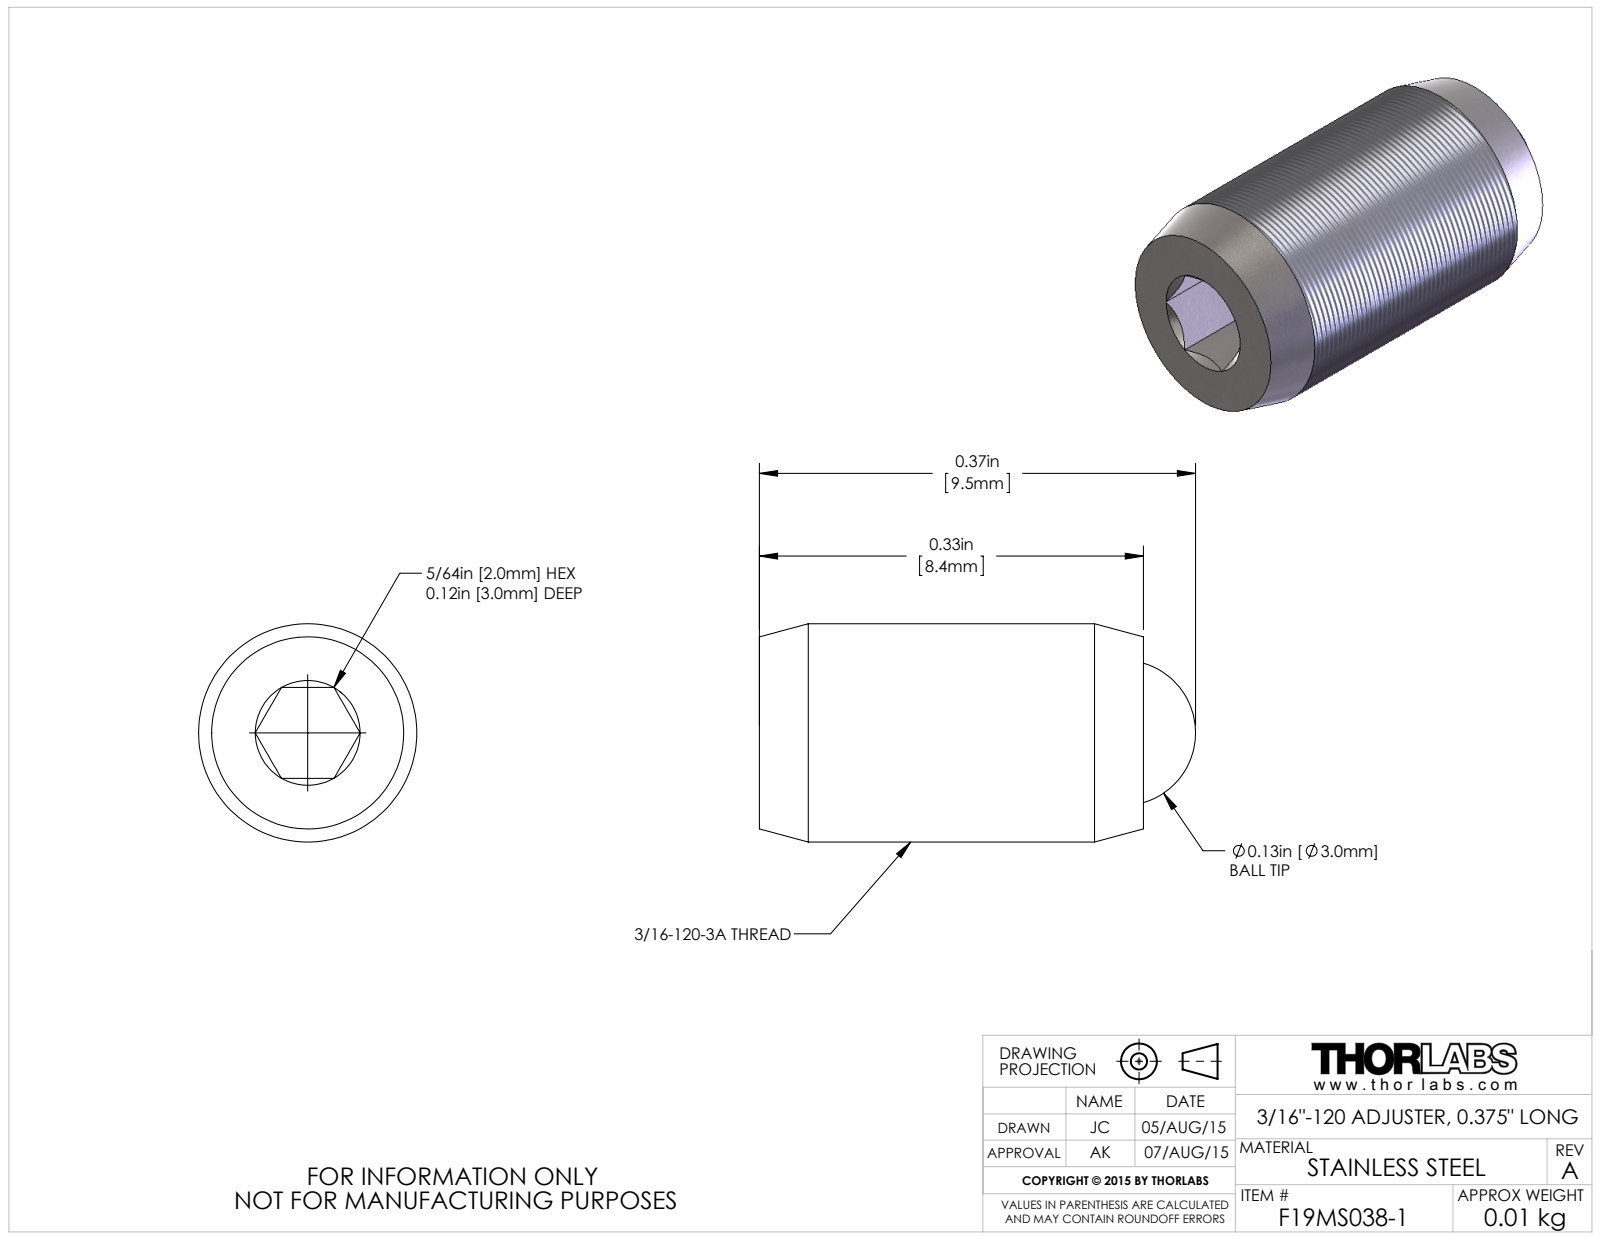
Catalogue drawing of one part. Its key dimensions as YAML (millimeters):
part_name: "TTN045702-E0W"
step_written_by: "SolidWorks 2014 (AUTOMOTIVE_DESIGN)"
units: millimeters
bodies: {solids: 2, faces: 29, planar: 9, cylindrical: 4, other: 16}
overall_size: [9.5, 4.8, 4.8]
volume: 100
surface_area: 219
round_holes:
  - {diameter: 3.2, count: 1}
round_bosses_or_shafts:
  - {diameter: 4.7, count: 1}
face_to_face_distances: [2, 8.4, 3, 5.3, 2]
